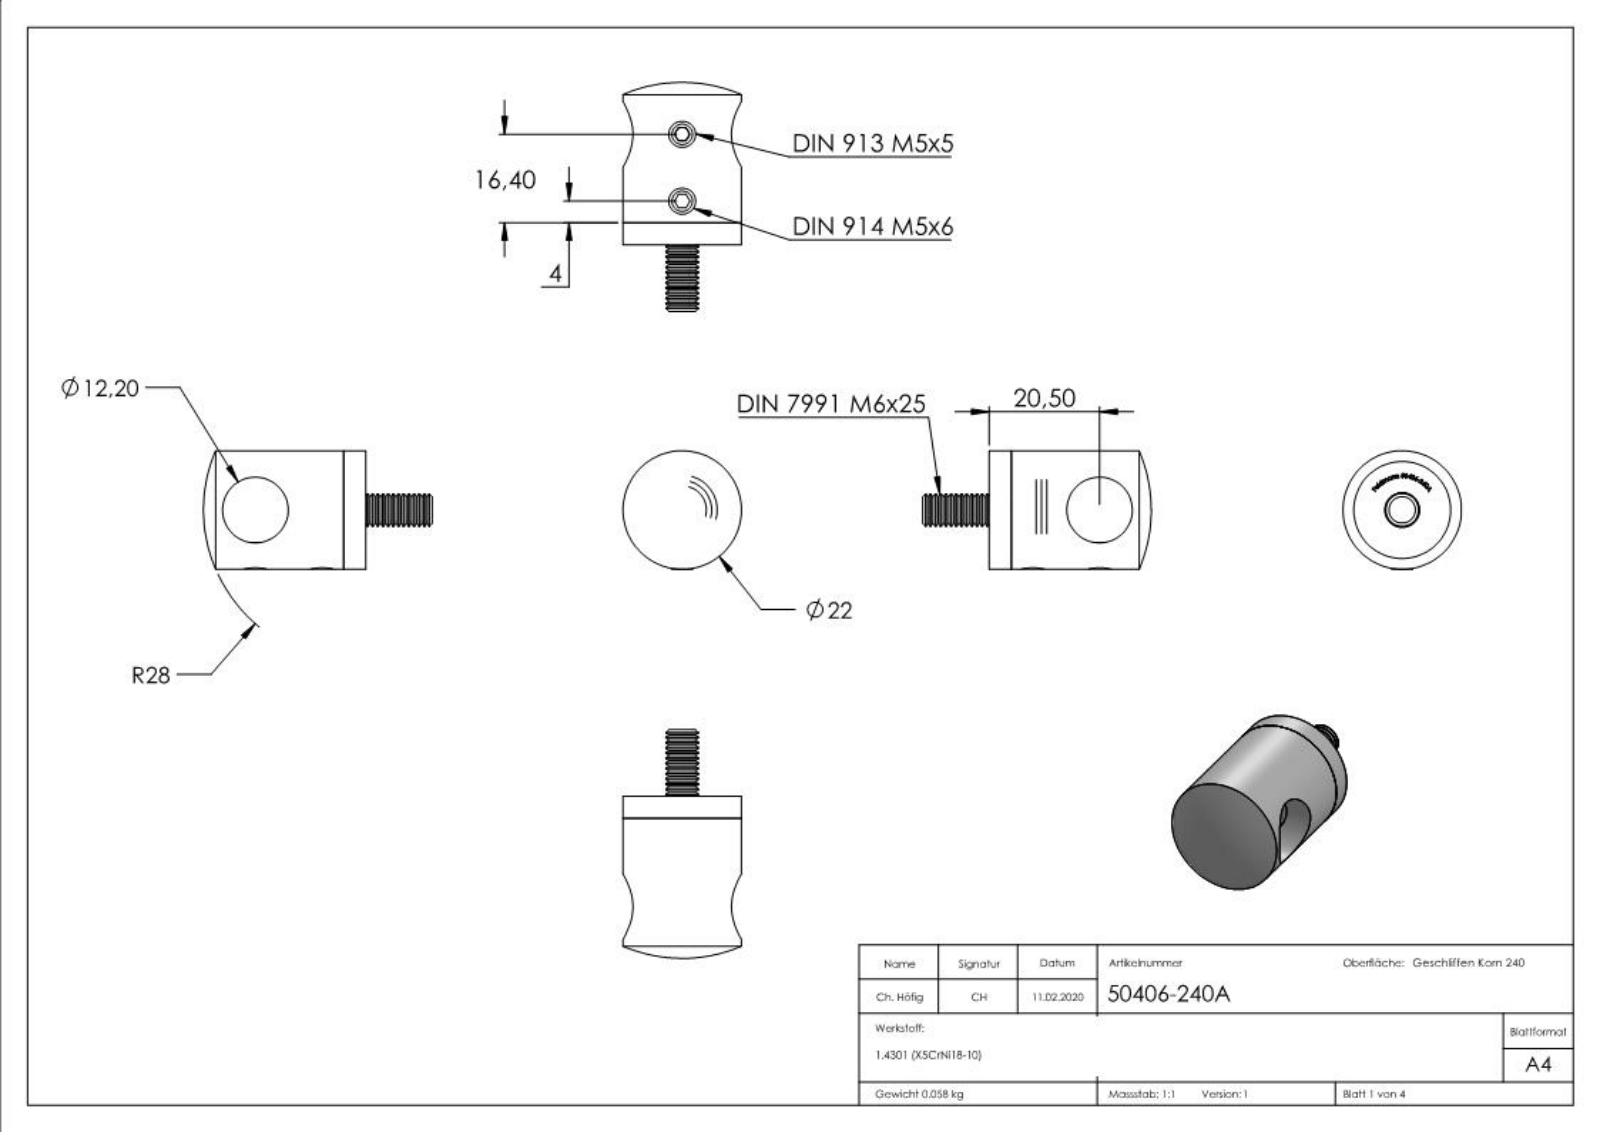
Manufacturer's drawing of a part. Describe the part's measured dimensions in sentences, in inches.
The part is named "socket countersunk head screw_din_DIN 7991 - M6 x 25 --- 25S; 50406-240A; DIN913_DIN 913 M5x5; Querstabhalter Teil2 Konfig (+7 more)". Its 3-D file was written by "SolidWorks 2015 (CONFIG_CONTROL_DESIGN)". It is 5 solids with 371 faces: 180 planar, 35 cylindrical and 156 other. Overall it measures 2.756 by 1.671 by 0.866 inches. Its volume is 0.486 cubic inches and its surface area 9.205 square inches. Round holes: 2 of diameter 0.165, 1 of diameter 0.256, 1 of diameter 0.472, 1 of diameter 0.48, 1 of diameter 0.709. Round bosses or shafts: 2 of diameter 0.197, 1 of diameter 0.866, 1 of diameter 0.469, 1 of diameter 0.456, 1 of diameter 0.236. The main face-to-face distances are 0.083, 0.079, 0.161, 0.498, 0.419, 0.337, 0.098, 0.457, 0.378, 0.295. The hole center spacings are 0.488.
